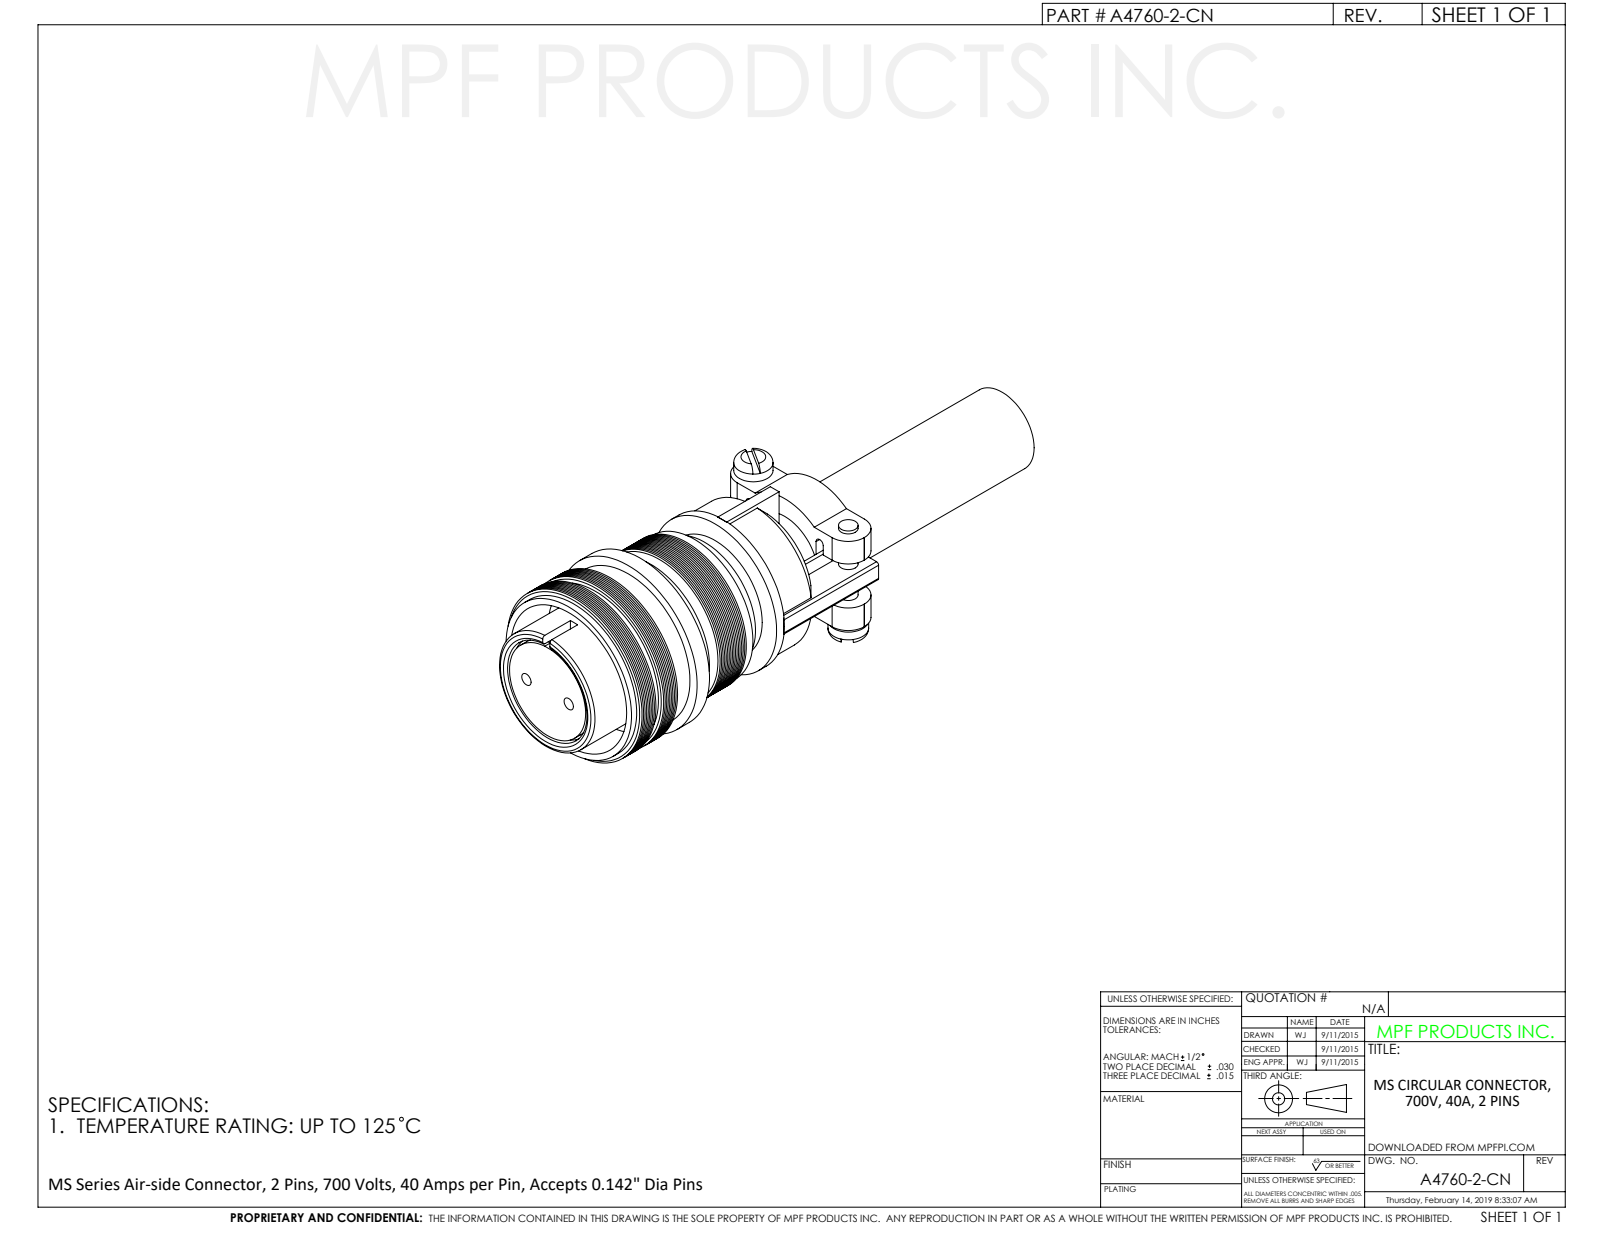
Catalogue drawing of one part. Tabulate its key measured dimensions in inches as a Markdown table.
| quantity | value |
| --- | --- |
| part name | A4760-2-CN |
| STEP written by | SolidWorks 2012 (CONFIG_CONTROL_DESIGN) |
| units | inches |
| bodies | 1 solid, 371 faces (105 planar, 84 cylindrical, 182 other) |
| overall size | 4.437 × 1.34 × 1.34 |
| volume | 2.395 in³ |
| surface area | 31.36 in² |
| round holes (diameter × count) | 0.091 × 2, 0.55 × 1, 0.78 × 1, 1.125 × 1 |
| round bosses / shafts (diameter × count) | 0.135 × 2, 1.34 × 1, 1.223 × 1, 1.22 × 1, 1.2 × 1, 1.14 × 1, 0.99 × 1, 0.92 × 1 |
| partial cylindrical surfaces (radius × count) | 0.034 × 8, 0.02 × 4, 0.156 × 4, 0.323 × 1, 0.472 × 1, 0.473 × 1 |
| main face-to-face distances | 1.193, 0.643, 0.47, 0.722, 0.1, 0.2, 2.096, 1.626, 0.904, 0.522 |
| hole center spacings | 0.206, 0.411 |
